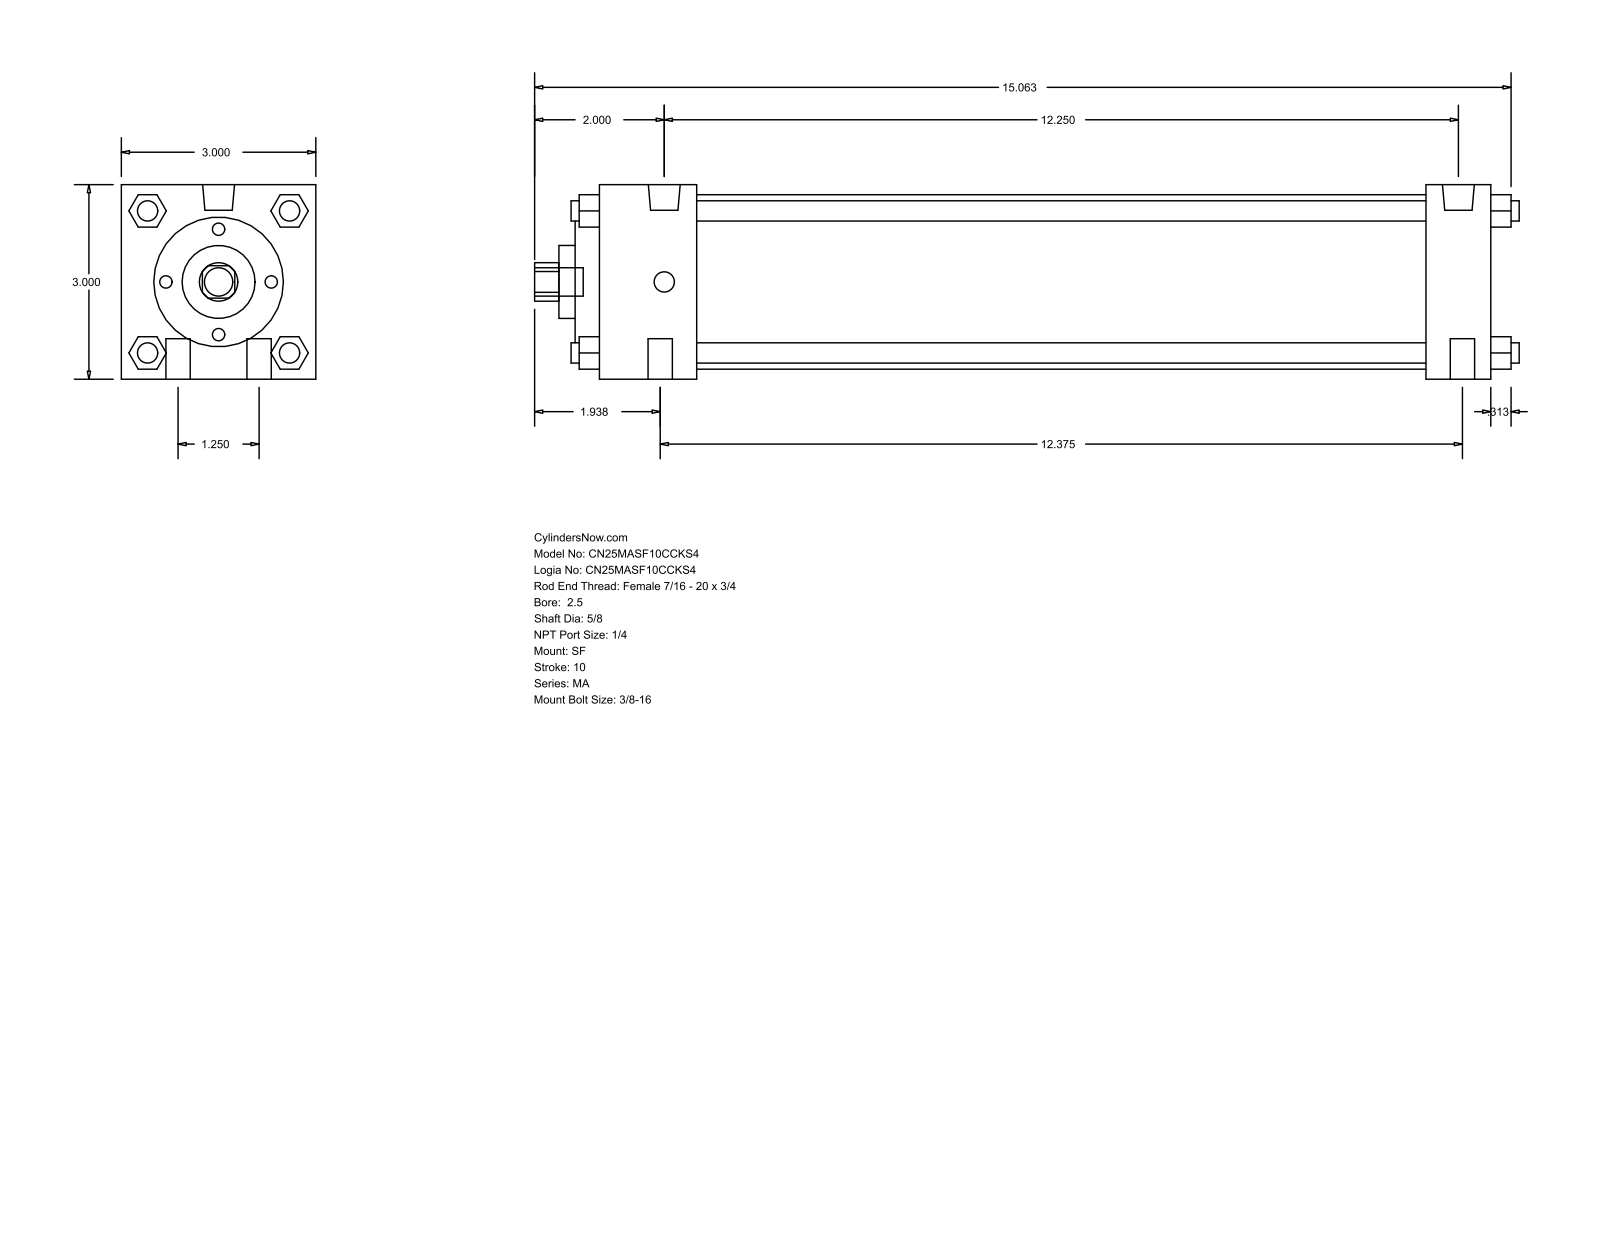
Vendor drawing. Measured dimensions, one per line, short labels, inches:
name: MA_SF__0250_0.625
written by: GSSL Pune (CONFIG_CONTROL_DESIGN)
unit: in
bodies: 0 solids, 126 faces (95 planar, 31 cylindrical, 0 other)
size: 15.187 × 3 × 3
holes: 1× ⌀0.625, 1× ⌀1.125, 1× ⌀2, 1× ⌀2.69
bosses: 6× ⌀0.313, 4× ⌀0.375, 2× ⌀0.492, 1× ⌀0.437
rounds: 1× R0.297
face distances: 3, 13.75, 1, 12.75, 1.5, 11.25, 12.25, 0.5, 0.375, 1.875
